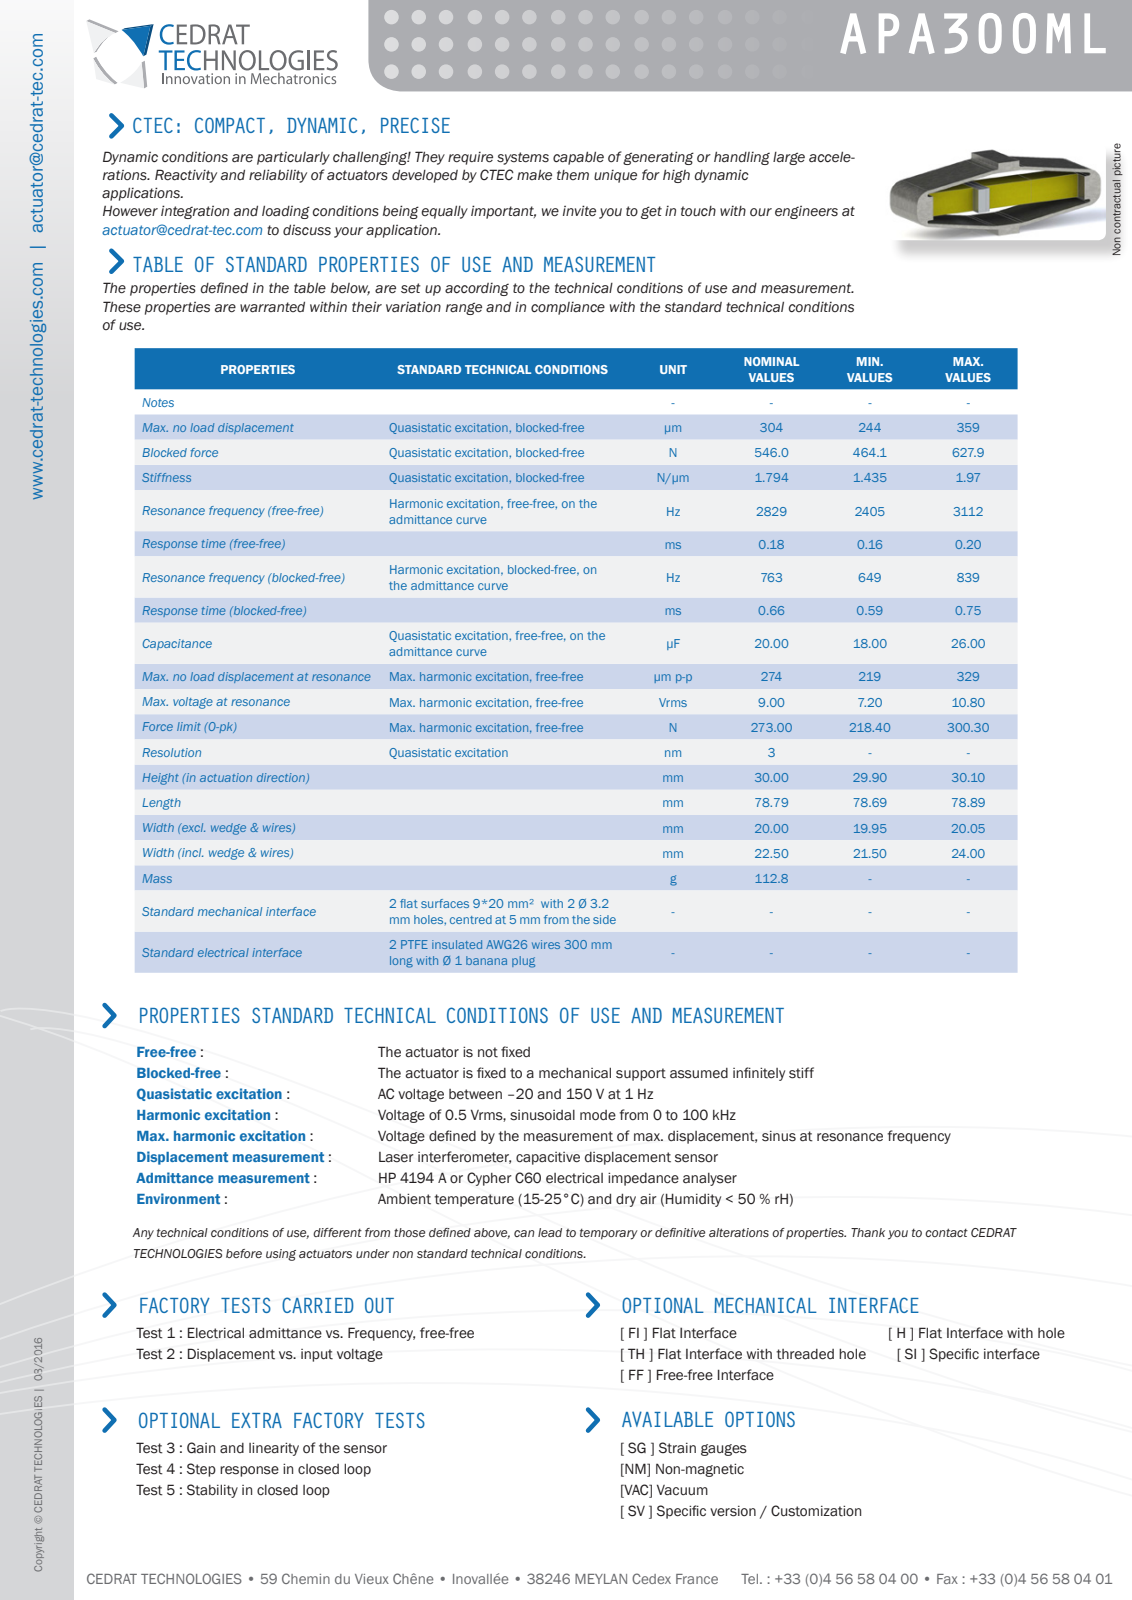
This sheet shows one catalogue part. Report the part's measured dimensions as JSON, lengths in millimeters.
{"part_name": "12600001", "step_written_by": "SolidWorks 2020 (AUTOMOTIVE_DESIGN)", "units": "millimeters", "bodies": {"solids": 2, "faces": 90, "planar": 48, "cylindrical": 34, "other": 8}, "overall_size": [78.79, 61, 20], "volume_mm3": 16363, "surface_area_mm2": 12614, "round_holes": [[5.8, 4], [2.5, 2]], "partial_cylinders_radius": [[0.6, 4], [0.7, 4], [5.86, 4], [9.6, 4], [11, 4]], "face_to_face_distances": [1.39, 25.87, 10, 24.48, 27.26, 5, 15, 20, 4.5, 6.36], "hole_center_spacings": [7.25, 51, 10, 45.5, 46.59, 56]}
